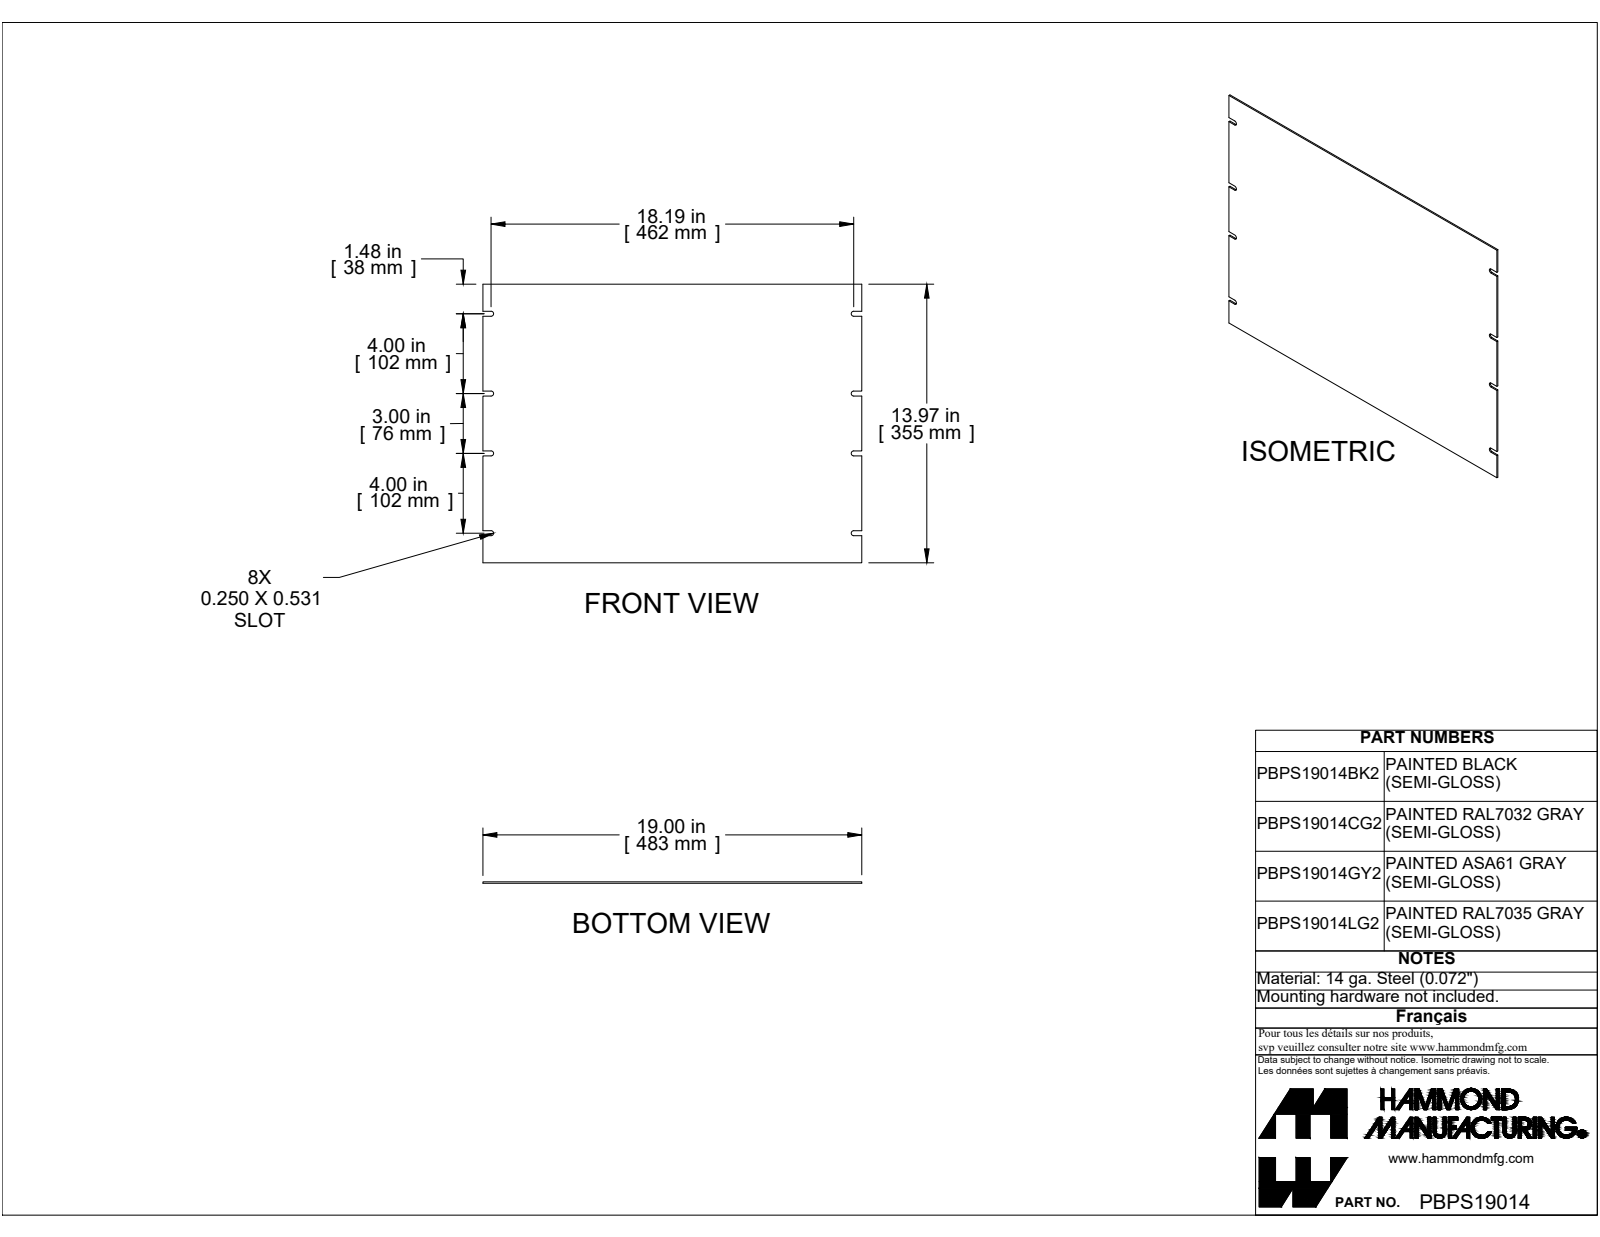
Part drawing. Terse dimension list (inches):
name: PBPS19014GY2
written by: SolidWorks 2019 (CONFIG_CONTROL_DESIGN)
unit: in
bodies: 1 solid, 38 faces (30 planar, 8 cylindrical, 0 other)
size: 19 × 13.968 × 0.072
volume: 19.04 in³; area: 534.1 in²
rounds: 8× R0.125
face distances: 0.072, 13.968, 19, 7, 4, 0.25, 0.25, 3, 1.609, 12.359
